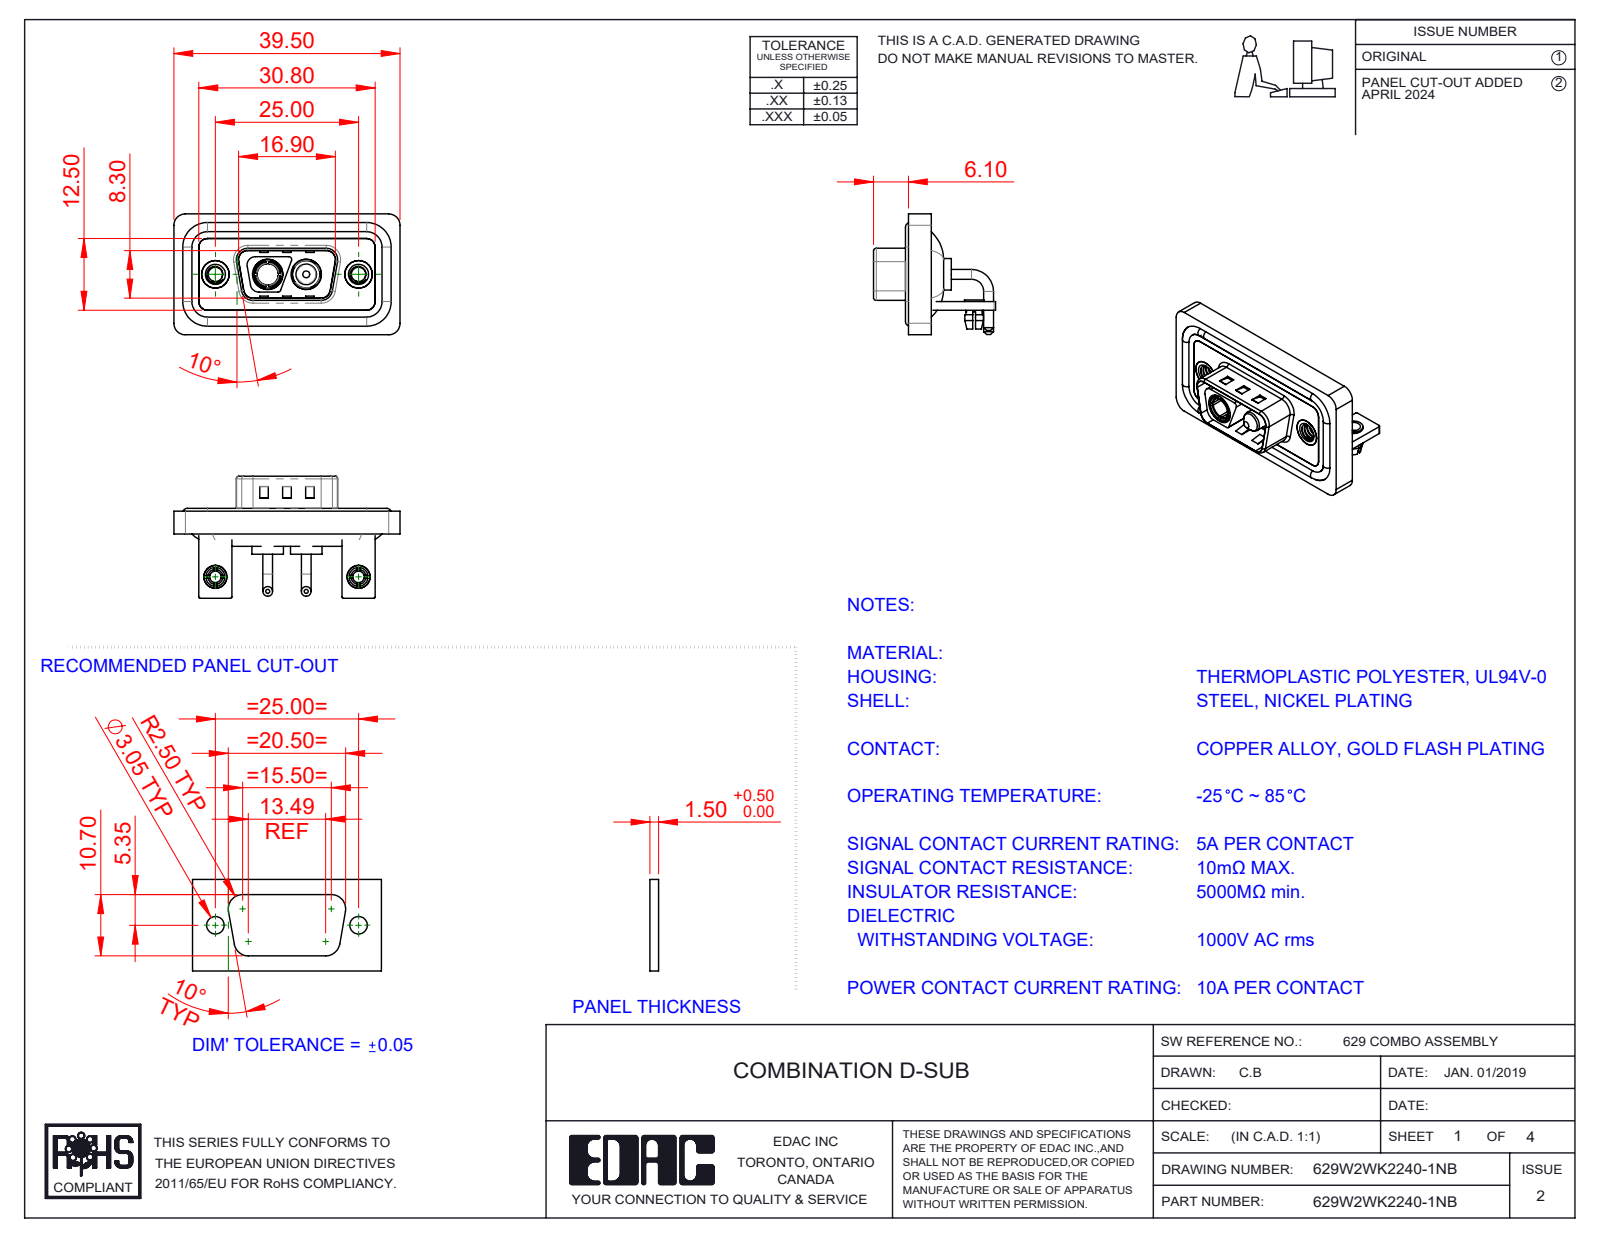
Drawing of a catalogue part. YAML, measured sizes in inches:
part_name: "629Combo Stabilizer Bracket; 629Combo Housing_2WK2; 629Combo Threaded Rivet_B; 629W2WK2140-1NB (+6 more)"
step_written_by: "SolidWorks 2023 (CONFIG_CONTROL_DESIGN)"
units: inches
bodies: {solids: 15, faces: 672, planar: 257, cylindrical: 281, other: 134}
overall_size: [1.555, 0.839, 0.831]
volume: 0.297
surface_area: 12.75
round_holes:
  - {diameter: 0.098, count: 4}
  - {diameter: 0.079, count: 2}
  - {diameter: 0.126, count: 2}
  - {diameter: 0.157, count: 2}
  - {diameter: 0.189, count: 2}
  - {diameter: 0.191, count: 2}
  - {diameter: 0.197, count: 2}
  - {diameter: 0.209, count: 2}
  - {diameter: 0.146, count: 1}
round_bosses_or_shafts:
  - {diameter: 0.067, count: 4}
  - {diameter: 0.063, count: 4}
  - {diameter: 0.217, count: 2}
  - {diameter: 0.205, count: 2}
  - {diameter: 0.193, count: 2}
  - {diameter: 0.187, count: 2}
  - {diameter: 0.157, count: 2}
  - {diameter: 0.148, count: 2}
partial_cylinders:
  - {radius: 0.059, count: 20}
  - {radius: 0.079, count: 19}
  - {radius: 0.01, count: 16}
  - {radius: 0.02, count: 11}
  - {radius: 0.063, count: 8}
  - {radius: 0.024, count: 4}
  - {radius: 0.026, count: 4}
  - {radius: 0.035, count: 4}
face_to_face_distances: [0.016, 0.059, 0.114, 0.031, 0.043, 0.047, 0.083, 0.063, 0.146, 0.098]
hole_center_spacings: [0.36, 0.624, 0.984, 0.265]
